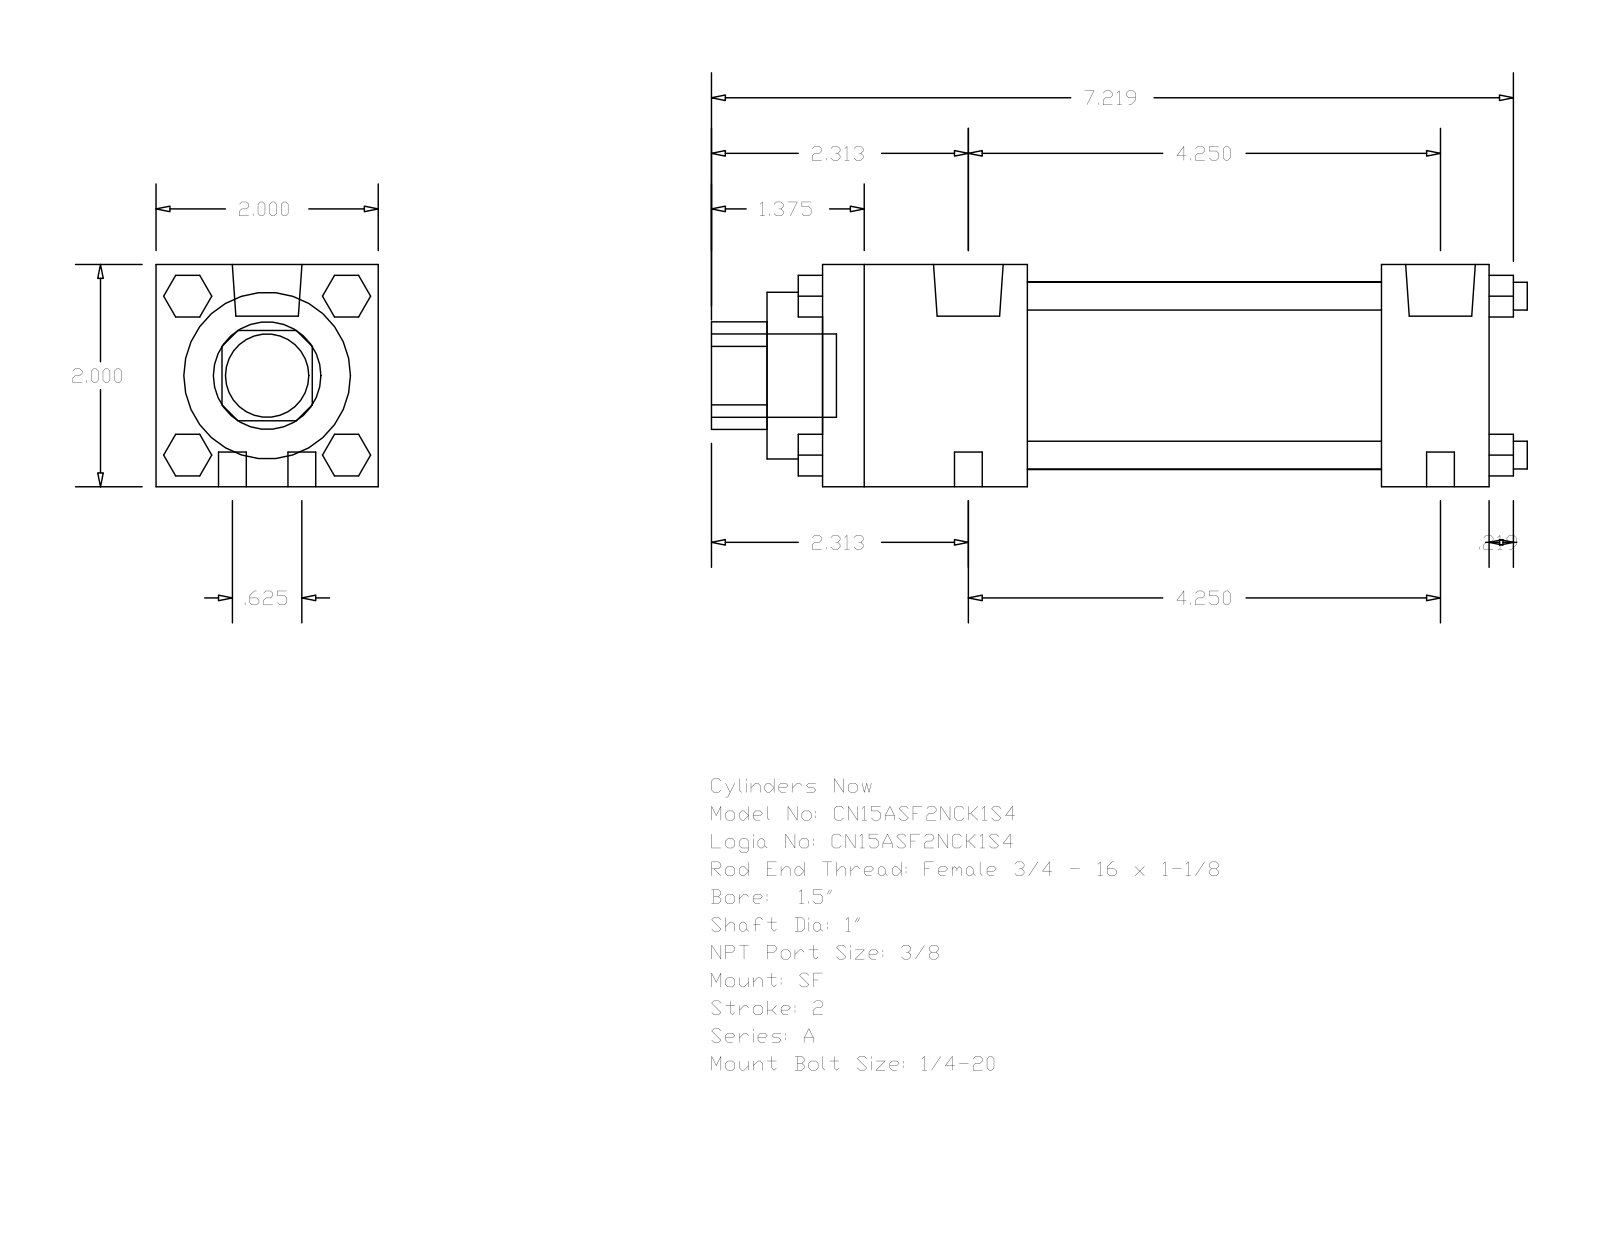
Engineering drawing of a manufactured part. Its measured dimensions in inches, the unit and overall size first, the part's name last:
Units: inches
Overall size (bounding box): 7.344 × 2 × 2
Round holes (diameter × count): ⌀1 ×1, ⌀1.5 ×1, ⌀1.69 ×1
Round bosses / shafts (diameter × count): ⌀0.25 ×8, ⌀0.627 ×2, ⌀0.219 ×2, ⌀0.75 ×1
Partial cylindrical surfaces — rounded edges, fillets, slot ends (radius × count): R0.484 ×1
Main face-to-face distances: 2, 6, 1.844, 5.031, 3.187, 4.156, 0.969, 0.5, 2.344, 5.531
Bodies: 0 solids, 124 faces (94 planar, 30 cylindrical, 0 other)
Part name (STEP PRODUCT): A_SF__0150_1
STEP written by: GSSL Pune (CONFIG_CONTROL_DESIGN)
